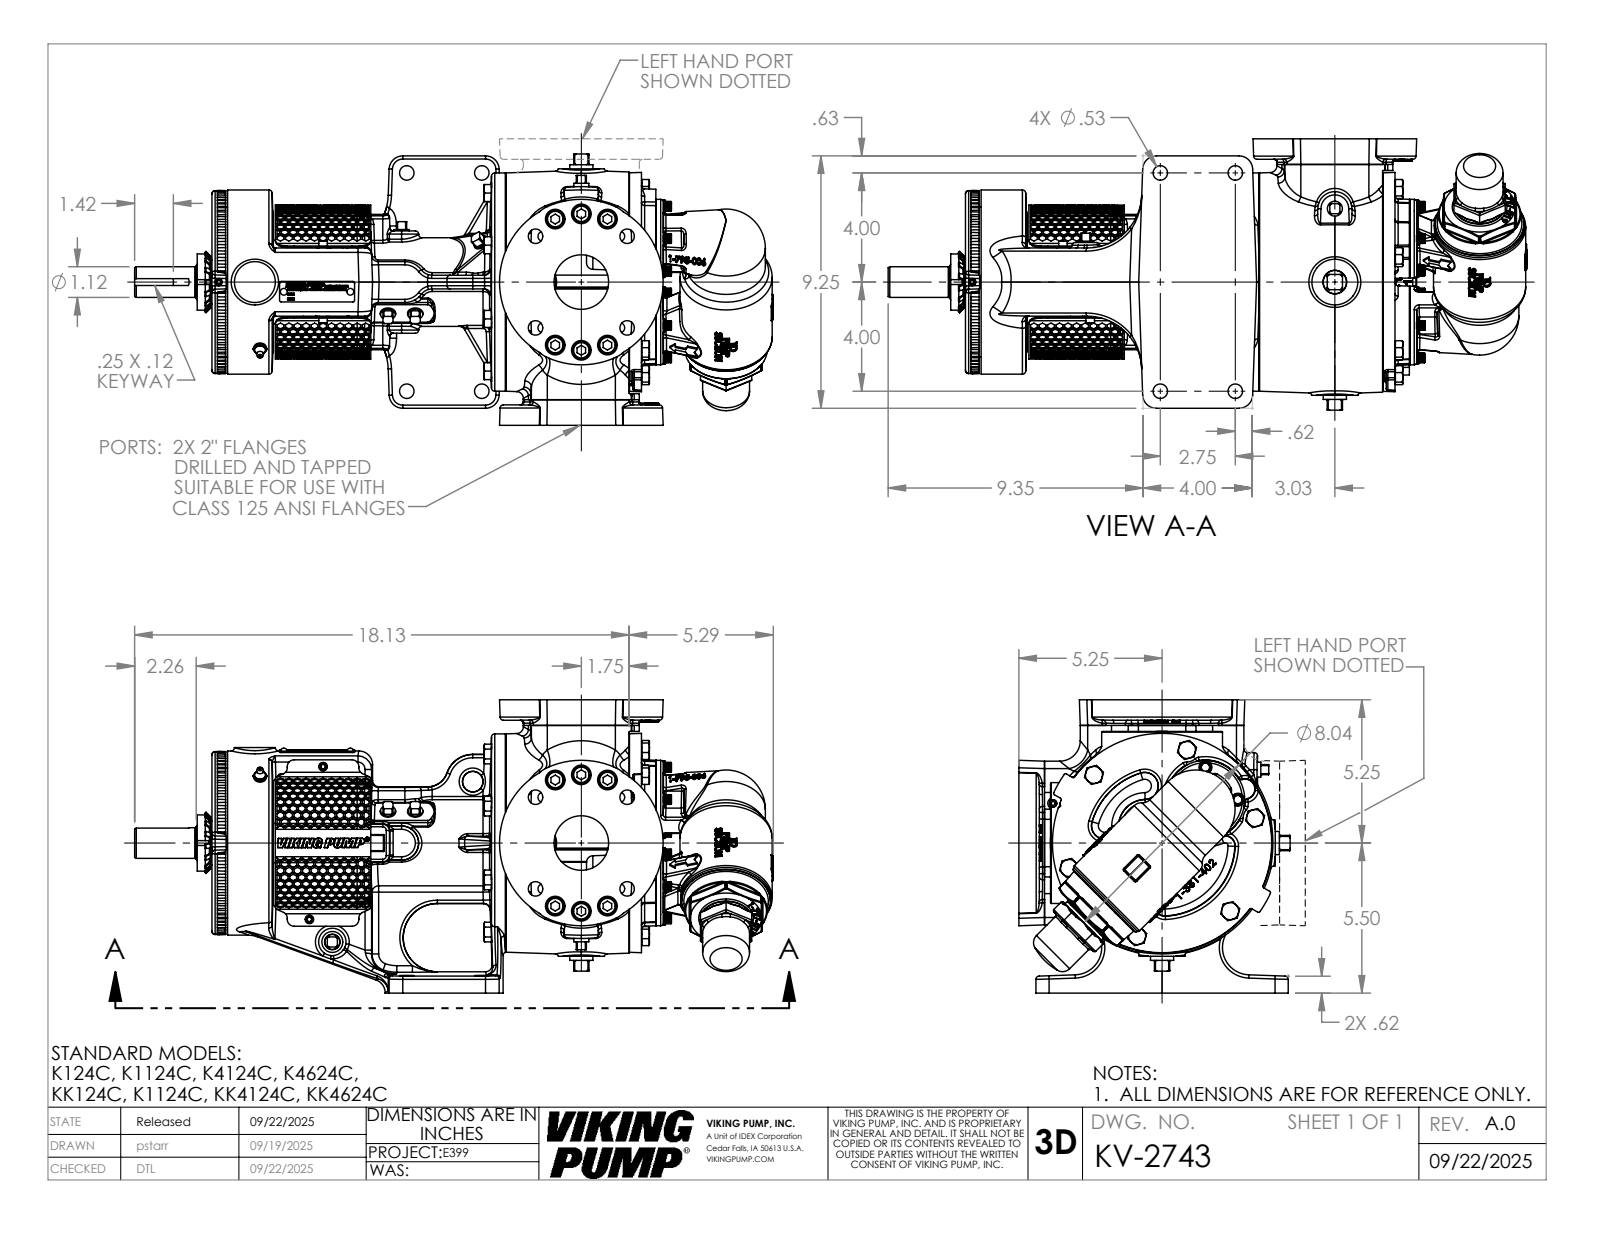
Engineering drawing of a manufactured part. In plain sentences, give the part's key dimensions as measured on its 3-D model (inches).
The part is named "KV-2743". Its 3-D file was written by "SolidWorks 2024 (AUTOMOTIVE_DESIGN)". It is 1 solid with 6353 faces: 2093 planar, 901 cylindrical and 3359 other. Overall it measures 23.417 by 10.75 by 9.945 inches. Its volume is 598.1 cubic inches and its surface area 1 123 square inches. Round holes: 12 of diameter 0.531, 12 of diameter 0.719, 9 of diameter 0.25, 8 of diameter 0.368, 8 of diameter 0.78, 6 of diameter 0.198, 2 of diameter 0.159, 2 of diameter 0.313, 2 of diameter 2, 1 of diameter 0.257, 1 of diameter 0.453, 1 of diameter 1.387. Round bosses or shafts: 23 of diameter 0.625, 8 of diameter 0.469, 3 of diameter 2.88, 3 of diameter 0.625, 3 of diameter 0.312, 3 of diameter 0.19, 2 of diameter 3.25, 1 of diameter 8. Partial cylindrical surfaces (rounded edges, fillets, slot ends): 96 of radius 0.01, 78 of radius 0.12, 37 of radius 0.03, 18 of radius 0.24, 18 of radius 1, 16 of radius 0.12, 10 of radius 0.25, 10 of radius 0.5. The main face-to-face distances are 10.75, 0.5, 15.749, 5.324, 10.425, 4.75, 0.574, 15.175, 0.75, 1. The hole center spacings are 3, 1.03, 2.5, 0.273, 0.976, 1.376, 2.187, 2.385.
